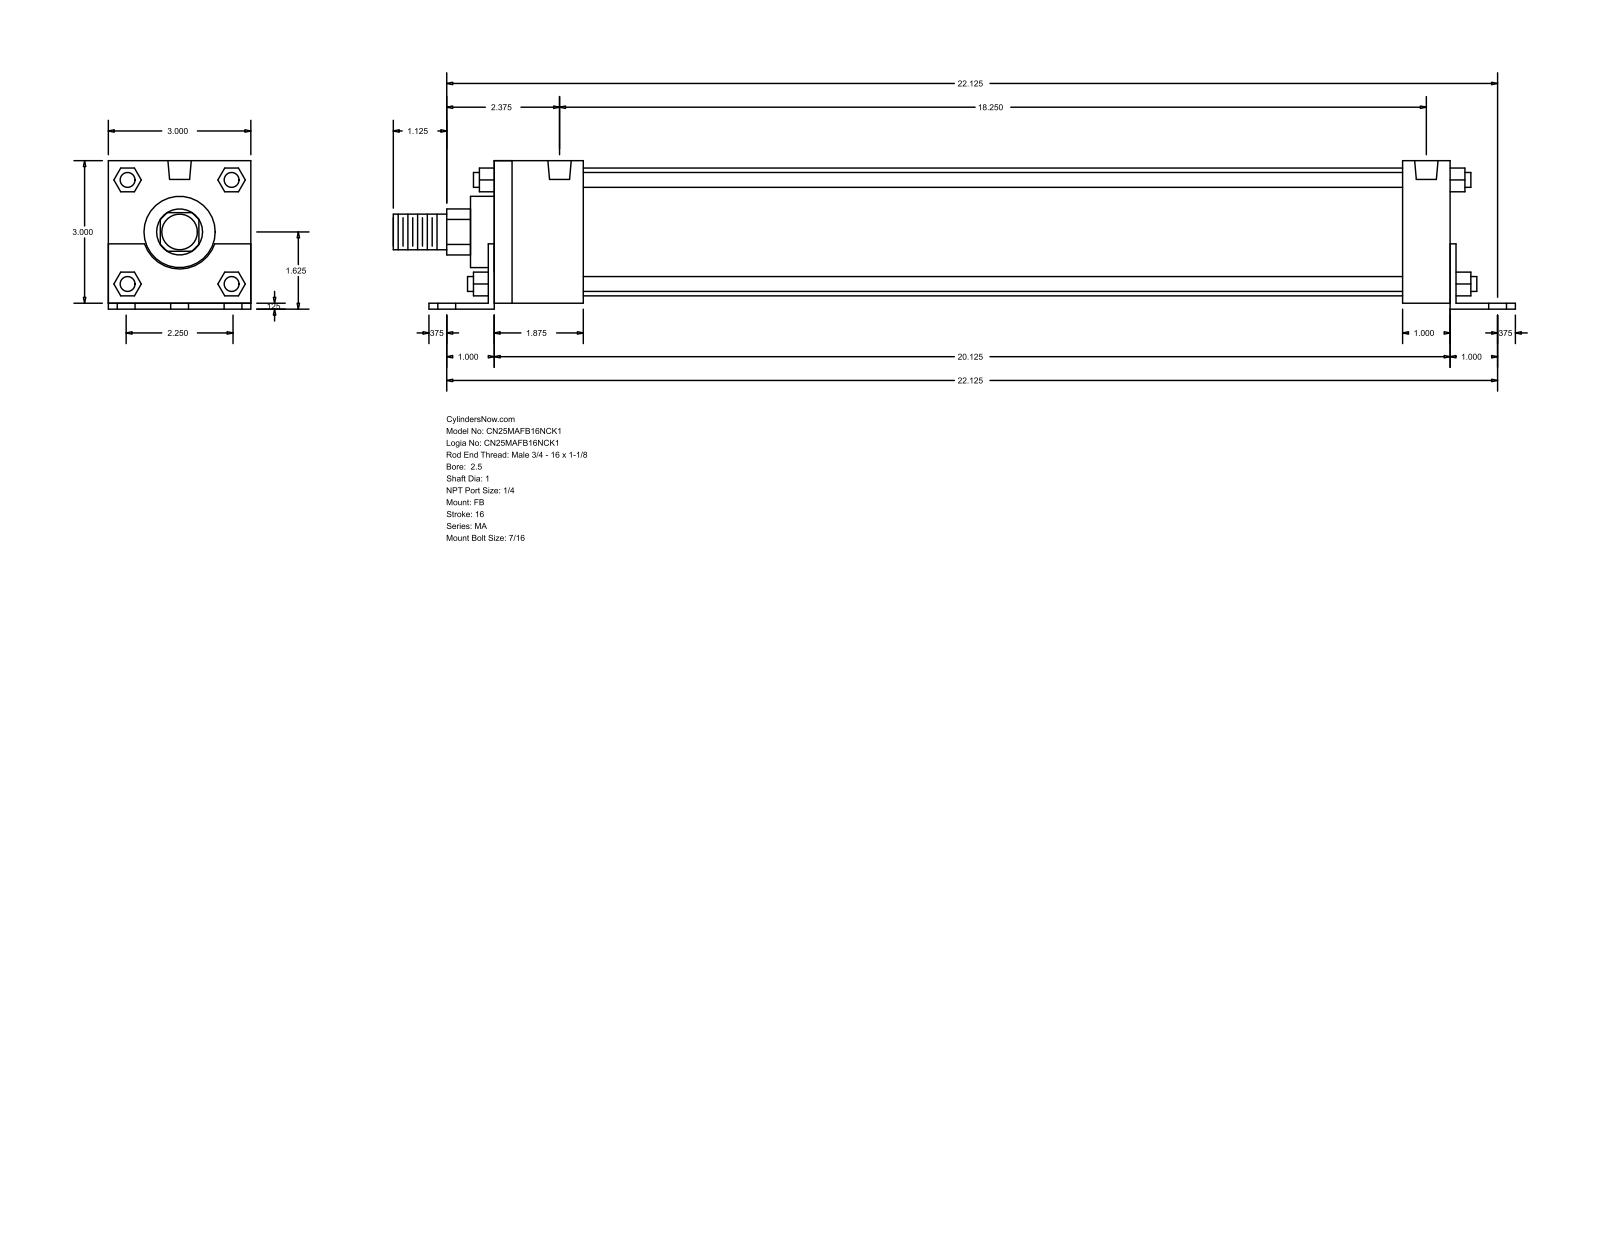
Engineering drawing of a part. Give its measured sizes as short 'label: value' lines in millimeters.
name: MA_FB__0250_1
written by: GSSL Pune (CONFIG_CONTROL_DESIGN)
unit: mm
bodies: 0 solids, 140 faces (105 planar, 35 cylindrical, 0 other)
size: 600.08 × 79.38 × 76.2
holes: 6× ⌀11.11, 4× ⌀7.94, 2× ⌀12.49
bosses: 4× ⌀7.94, 1× ⌀68.33, 1× ⌀38.1, 1× ⌀25.4, 1× ⌀19.05
rounds: 1× R12.29, 1× R19.81
face distances: 76.2, 3.17, 79.37, 514.35, 511.18, 12.7, 28.57, 25.4, 50.8, 47.63
hole spacings: 28.57, 562.71, 561.98, 47.62, 57.14, 66.75, 463.55, 502.46
